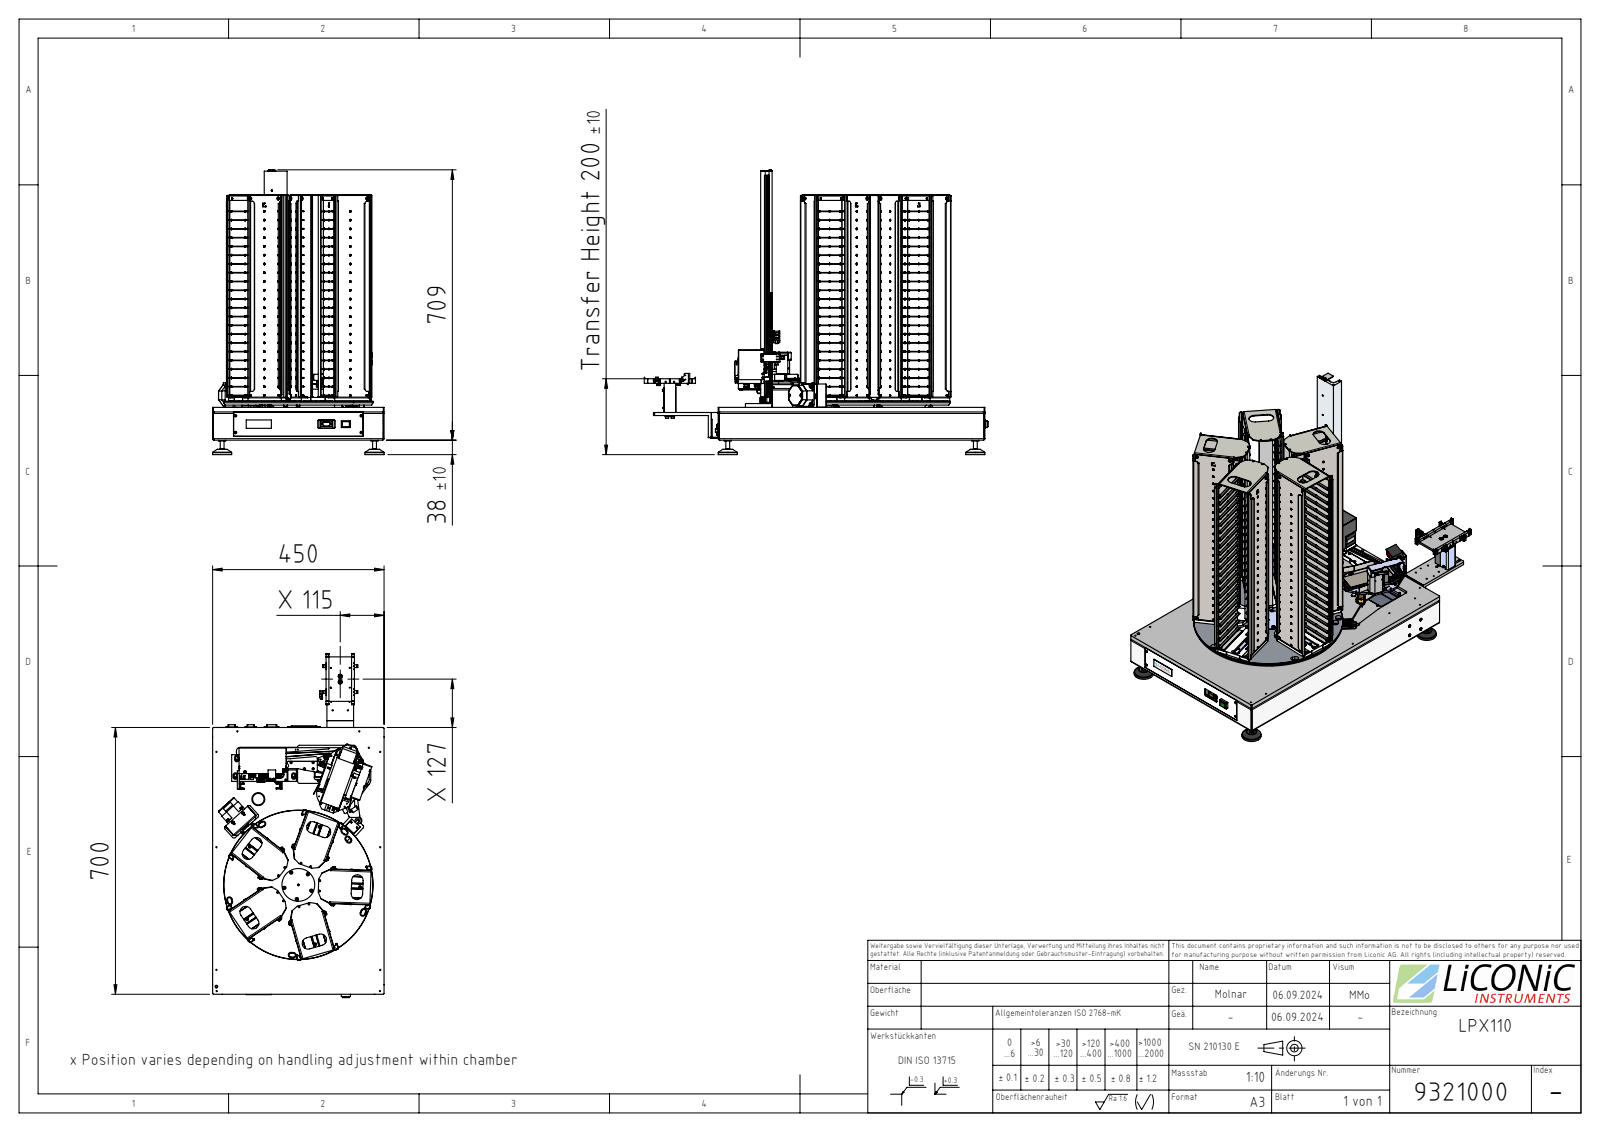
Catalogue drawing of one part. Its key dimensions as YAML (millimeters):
part_name: "9321000"
step_written_by: "SolidWorks 2022 (AUTOMOTIVE_DESIGN)"
units: millimeters
bodies: {solids: 34, faces: 5540, planar: 3098, cylindrical: 2341, other: 101}
overall_size: [902.84, 743.8, 450.01]
volume: 6877000
surface_area: 2656000
round_holes:
  - {diameter: 4, count: 50}
  - {diameter: 2.5, count: 49}
  - {diameter: 3.3, count: 25}
  - {diameter: 4.2, count: 23}
  - {diameter: 3, count: 12}
  - {diameter: 6.5, count: 11}
  - {diameter: 6, count: 10}
  - {diameter: 3.1, count: 8}
  - {diameter: 7.1, count: 8}
  - {diameter: 12, count: 7}
  - {diameter: 3.4, count: 6}
  - {diameter: 5.3, count: 6}
round_bosses_or_shafts:
  - {diameter: 50.01, count: 4}
  - {diameter: 10, count: 4}
  - {diameter: 1.5, count: 3}
  - {diameter: 392, count: 1}
  - {diameter: 86, count: 1}
  - {diameter: 15.5, count: 1}
  - {diameter: 14.5, count: 1}
partial_cylinders:
  - {radius: 0.1, count: 572}
  - {radius: 0.25, count: 572}
  - {radius: 2, count: 255}
  - {radius: 2.5, count: 110}
  - {radius: 5, count: 65}
  - {radius: 1, count: 56}
  - {radius: 3, count: 18}
  - {radius: 4, count: 16}
face_to_face_distances: [2, 72, 74, 12, 86, 84, 6, 1, 10, 28]
hole_center_spacings: [23, 46, 69, 92, 115, 138, 161, 184]
